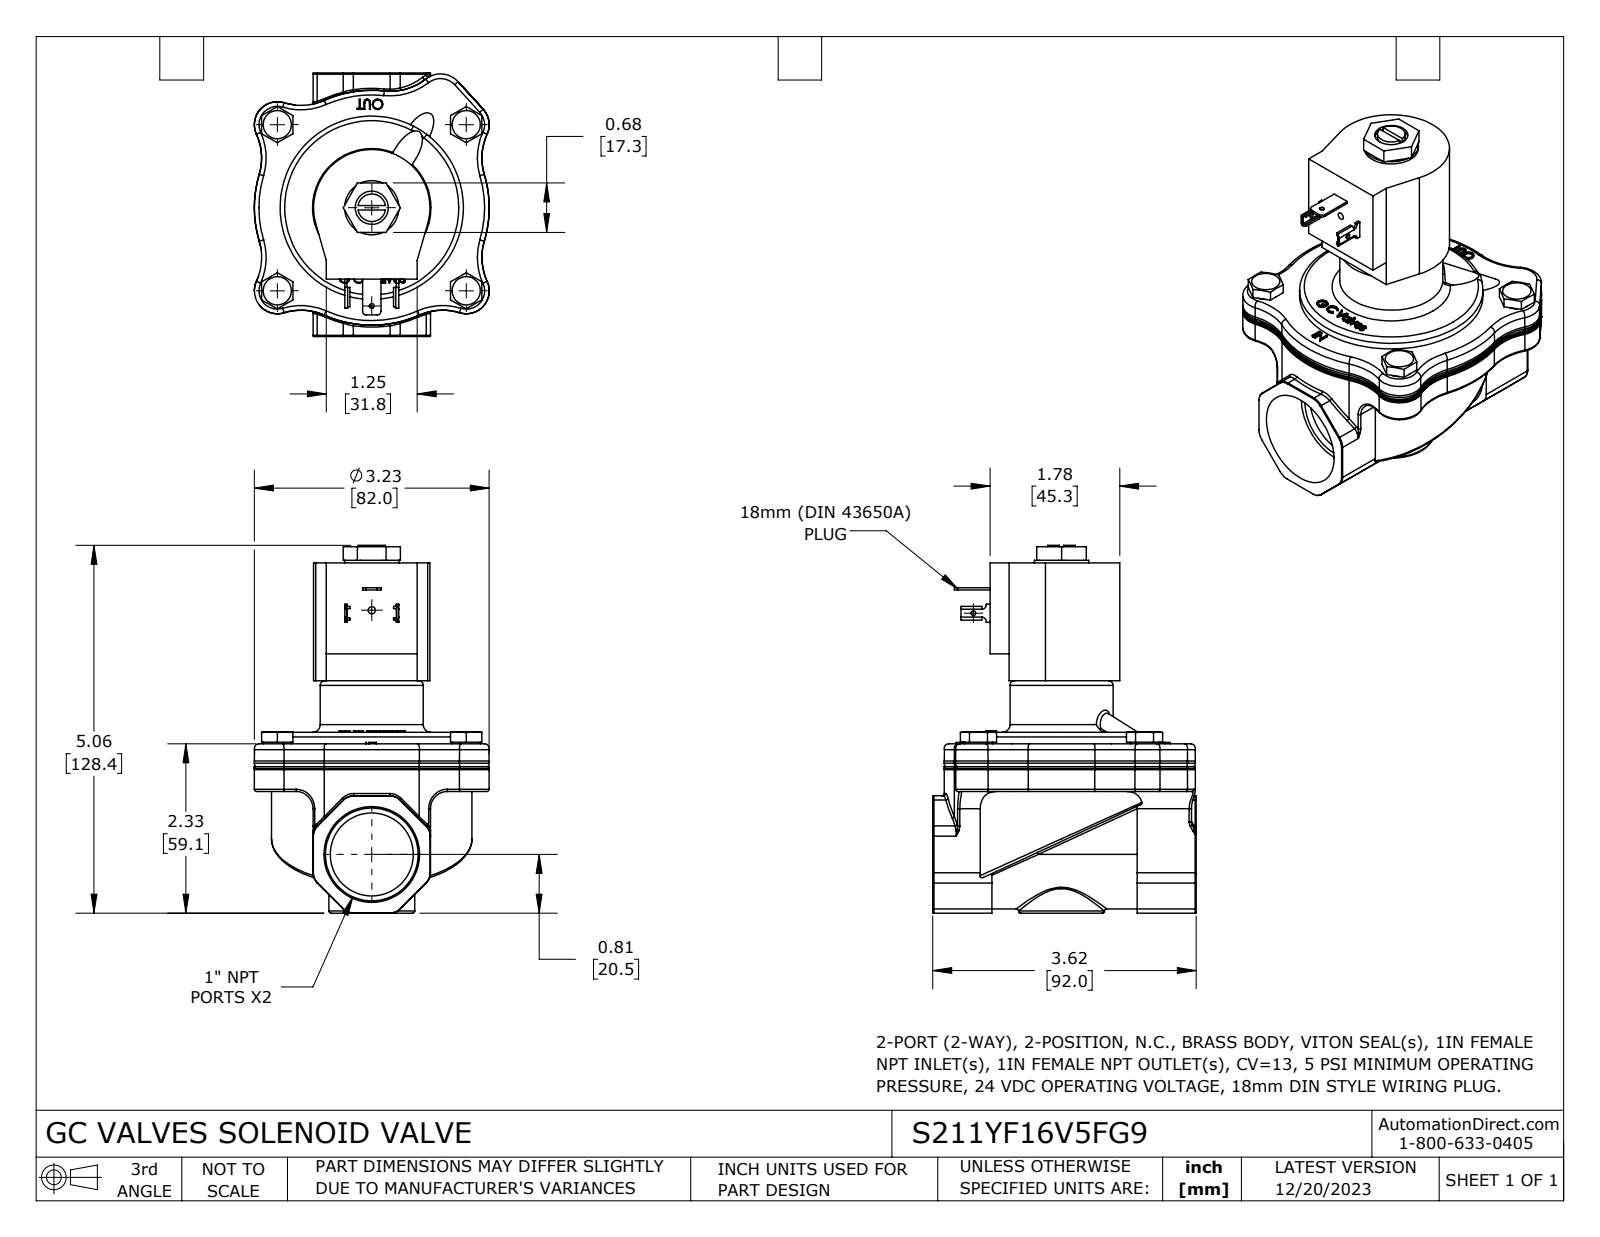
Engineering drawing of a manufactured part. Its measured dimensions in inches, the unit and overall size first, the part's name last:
Units: inches
Overall size (bounding box): 5.055 × 3.622 × 3.232
Round holes (diameter × count): ⌀0.066 ×1, ⌀0.067 ×1, ⌀0.1 ×1, ⌀0.456 ×1, ⌀1.141 ×1
Round bosses / shafts (diameter × count): ⌀0.388 ×4, ⌀2.52 ×1, ⌀1.417 ×1, ⌀1.181 ×1, ⌀0.746 ×1, ⌀0.38 ×1
Partial cylindrical surfaces — rounded edges, fillets, slot ends (radius × count): R0.031 ×24, R0.787 ×24, R0.315 ×12, R0.197 ×8, R0.006 ×4, R0.041 ×4, R0.05 ×2, R0.06 ×2
Main face-to-face distances: 0.157, 0.655, 0.812, 3.141, 2.486, 2.329, 2.485, 2.328, 1.673, 4.814
Hole centre spacings: 1.35, 3.356
Volume: 19.67 in³ · Surface area: 68.51 in²
Bodies: 1 solid, 671 faces (220 planar, 172 cylindrical, 279 other)
Part name (STEP PRODUCT): S211YF16V5FG9
STEP written by: SolidWorks 2023 (CONFIG_CONTROL_DESIGN)
